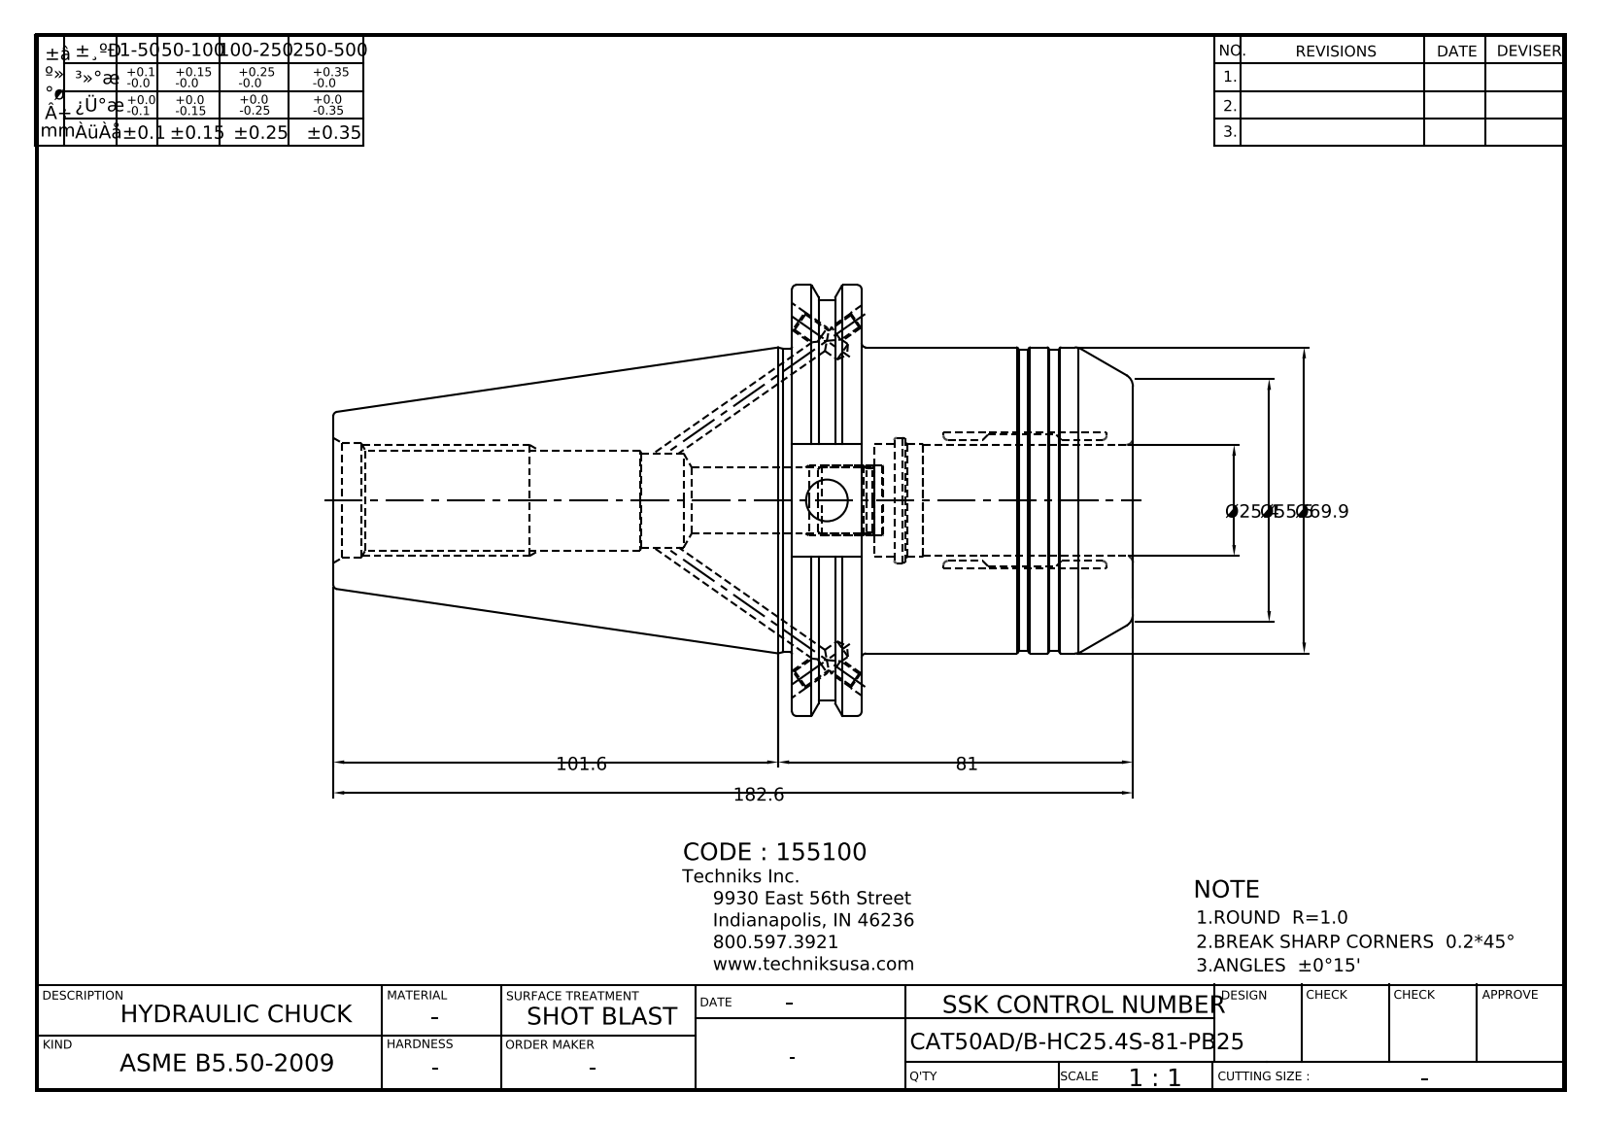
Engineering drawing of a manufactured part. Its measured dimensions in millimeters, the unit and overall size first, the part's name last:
Units: millimetres
Overall size (bounding box): 182.6 × 98.42 × 94.37
Round holes (diameter × count): ⌀5 ×3, ⌀4.3 ×2, ⌀9.53 ×1, ⌀15 ×1, ⌀16 ×1, ⌀20.5 ×1, ⌀22.23 ×1, ⌀25.4 ×1, ⌀25.8 ×1, ⌀26.2 ×1
Round bosses / shafts (diameter × count): ⌀98.42 ×1, ⌀91.29 ×1, ⌀69.9 ×1, ⌀69.25 ×1, ⌀68.9 ×1
Main face-to-face distances: 15.9, 77.85, 61.95, 104.75, 120.65, 182.6, 123.6, 18.85, 2.95, 59
Volume: 523 385 mm³ · Surface area: 65 494 mm²
Bodies: 1 solid, 150 faces (36 planar, 52 cylindrical, 62 other)
Part name (STEP PRODUCT): CAT50ADB-SHANK_20150526
STEP written by: CREO PARAMETRIC BY PTC INC, 2018500 (CONFIG_CONTROL_DESIGN)
